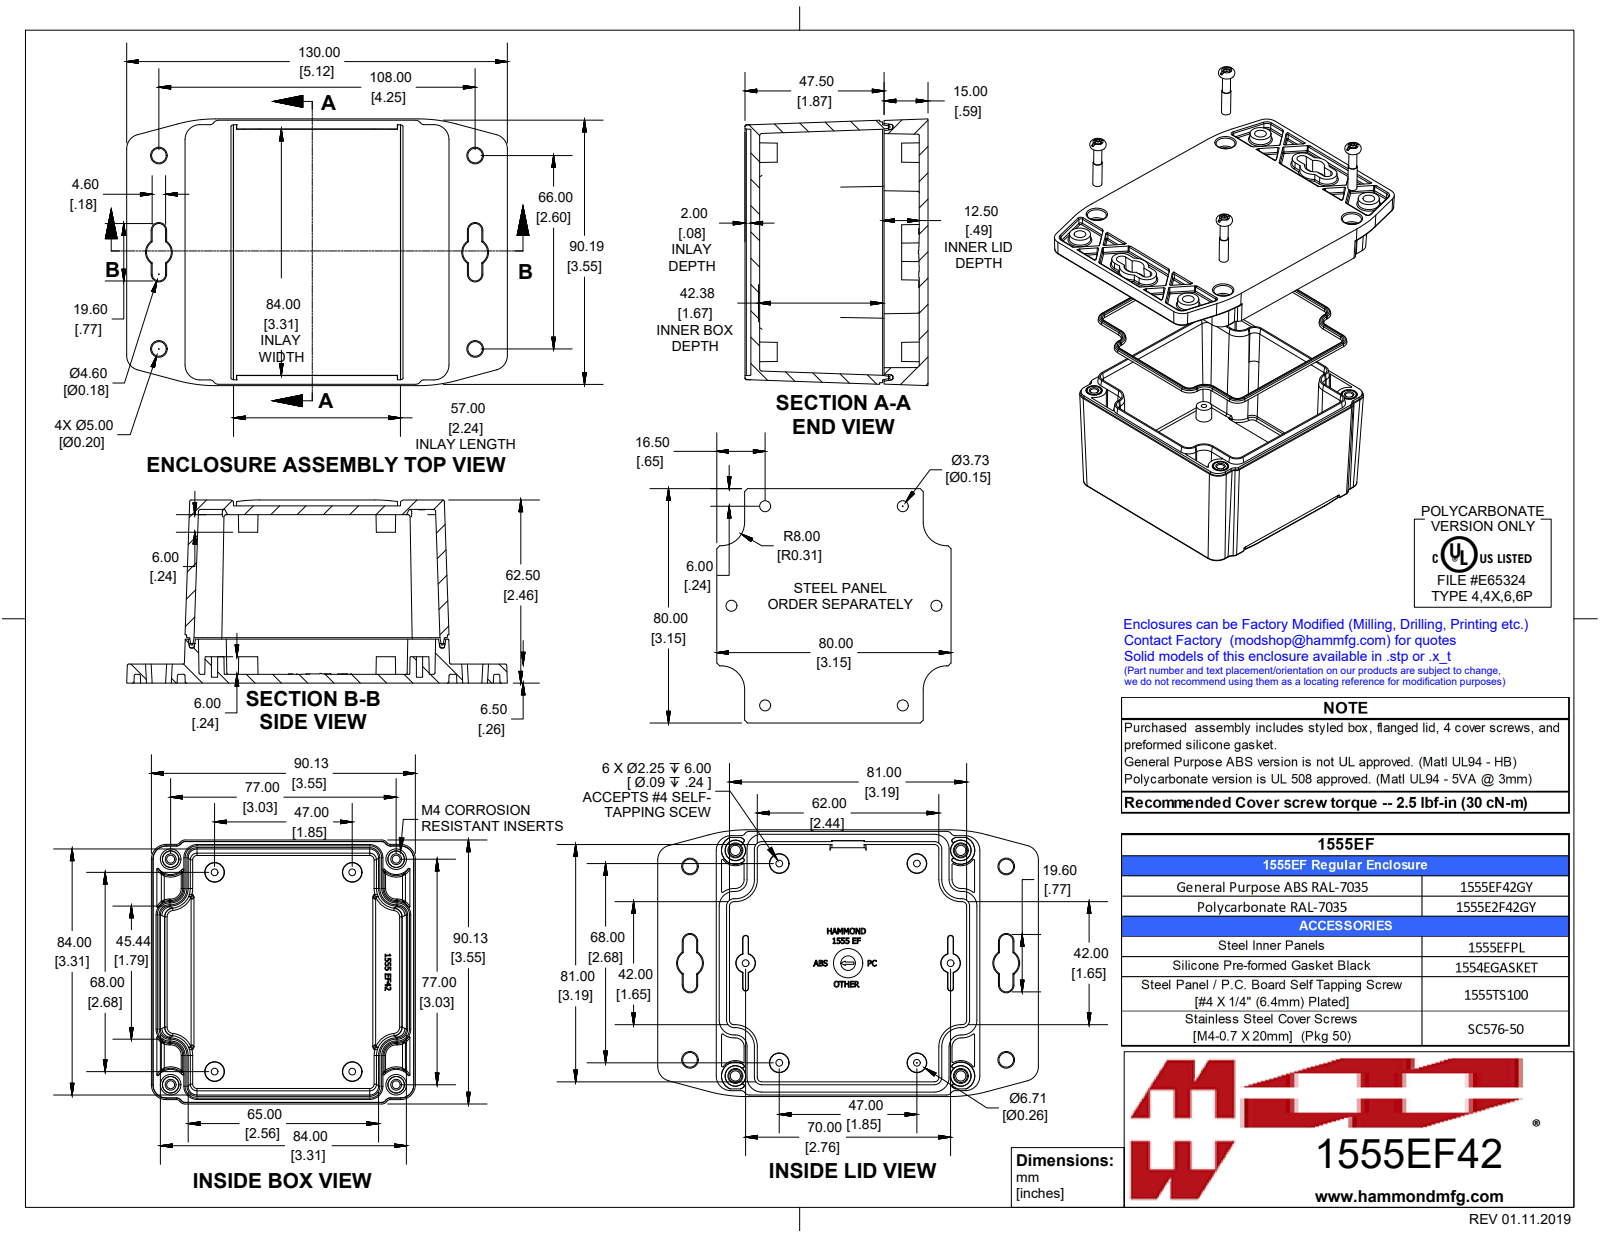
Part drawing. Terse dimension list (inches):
name: 1555E2F42GY
written by: SolidWorks 2019 (CONFIG_CONTROL_DESIGN)
unit: in
bodies: 11 solids, 2409 faces (783 planar, 490 cylindrical, 1136 other)
size: 5.118 × 3.585 × 2.461
volume: 8.781 in³; area: 155.8 in²
holes: 6× ⌀0.091, 4× ⌀0.128, 4× ⌀0.276
bosses: 4× ⌀0.25, 4× ⌀0.218, 4× ⌀0.21, 4× ⌀0.153, 4× ⌀0.135, 1× ⌀0.394, 1× ⌀0.197
rounds: 165× R0.02, 13× R0.031, 6× R0.012, 4× R0.118, 4× R0.197, 4× R0.201, 4× R1.969, 2× R0.039
face distances: 0.118, 2.264, 0.122, 2.382, 2.146, 0.079, 0.256, 0.117, 0.138, 2.008
hole spacings: 0.617, 1.413, 1.522, 2.447, 2.664, 2.915, 3.031, 3.267
